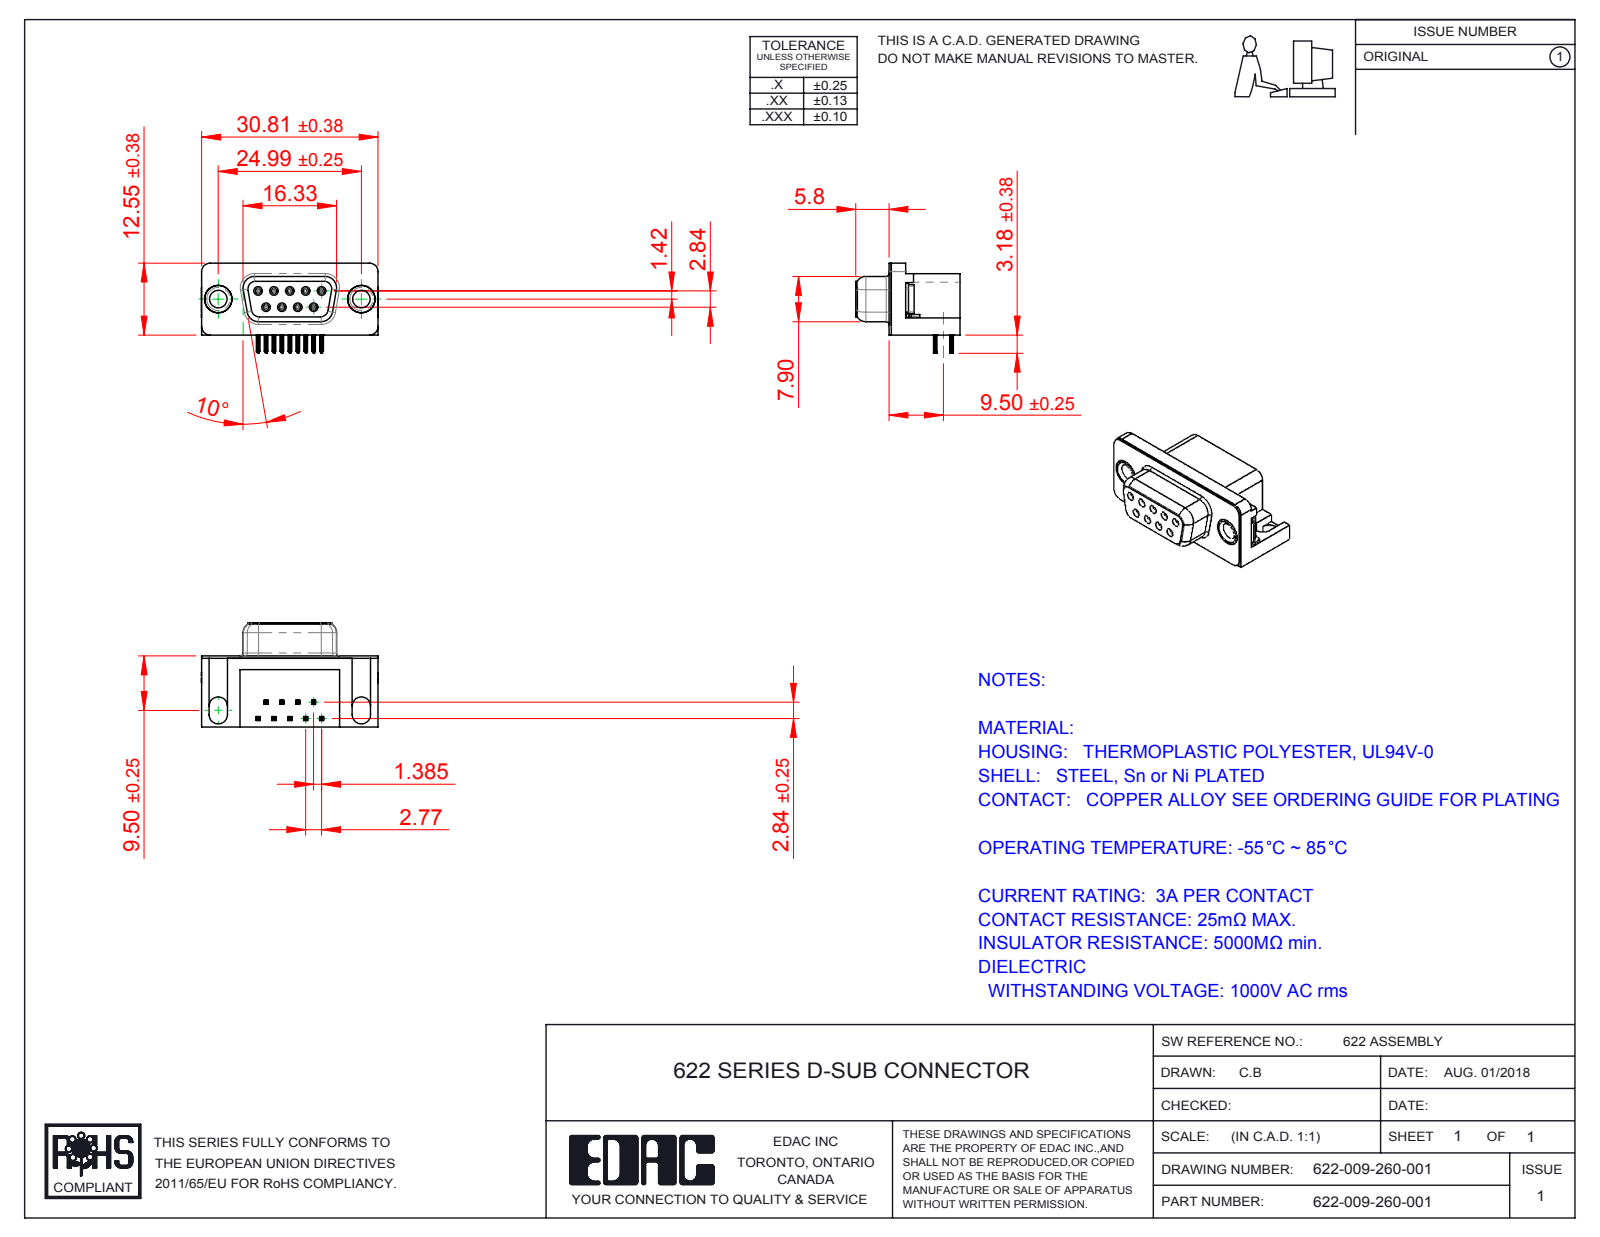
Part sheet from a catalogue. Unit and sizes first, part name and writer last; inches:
Units: inches
Overall size (bounding box): 1.216 × 0.717 × 0.619
Round holes (diameter × count): ⌀0.031 ×9, ⌀0.035 ×9, ⌀0.12 ×2, ⌀0.157 ×2, ⌀0.189 ×2, ⌀0.197 ×2
Round bosses / shafts (diameter × count): ⌀0.047 ×9, ⌀0.193 ×2, ⌀0.187 ×2, ⌀0.152 ×2
Partial cylindrical surfaces — rounded edges, fillets, slot ends (radius × count): R0.004 ×72, R0.006 ×36, R0.014 ×18, R0.039 ×18, R0.013 ×9, R0.01 ×8, R0.053 ×8, R0.063 ×8
Main face-to-face distances: 0.016, 0.472, 0.488, 0.114, 0.098, 0.244, 0.407, 0.014, 0.374, 0.421
Hole centre spacings: 0.124, 0.109, 0.218, 0.198, 0.198, 0.327, 0.294, 0.295
Volume: 0.224 in³ · Surface area: 7.559 in²
Bodies: 15 solids, 1528 faces (684 planar, 394 cylindrical, 450 other)
Part name (STEP PRODUCT): 622-009-260-001; 622 Socket Bottom; 622 Shell_9 Socket; 622 Non Board Mount (+3 more)
STEP written by: SolidWorks 2016 (CONFIG_CONTROL_DESIGN)
